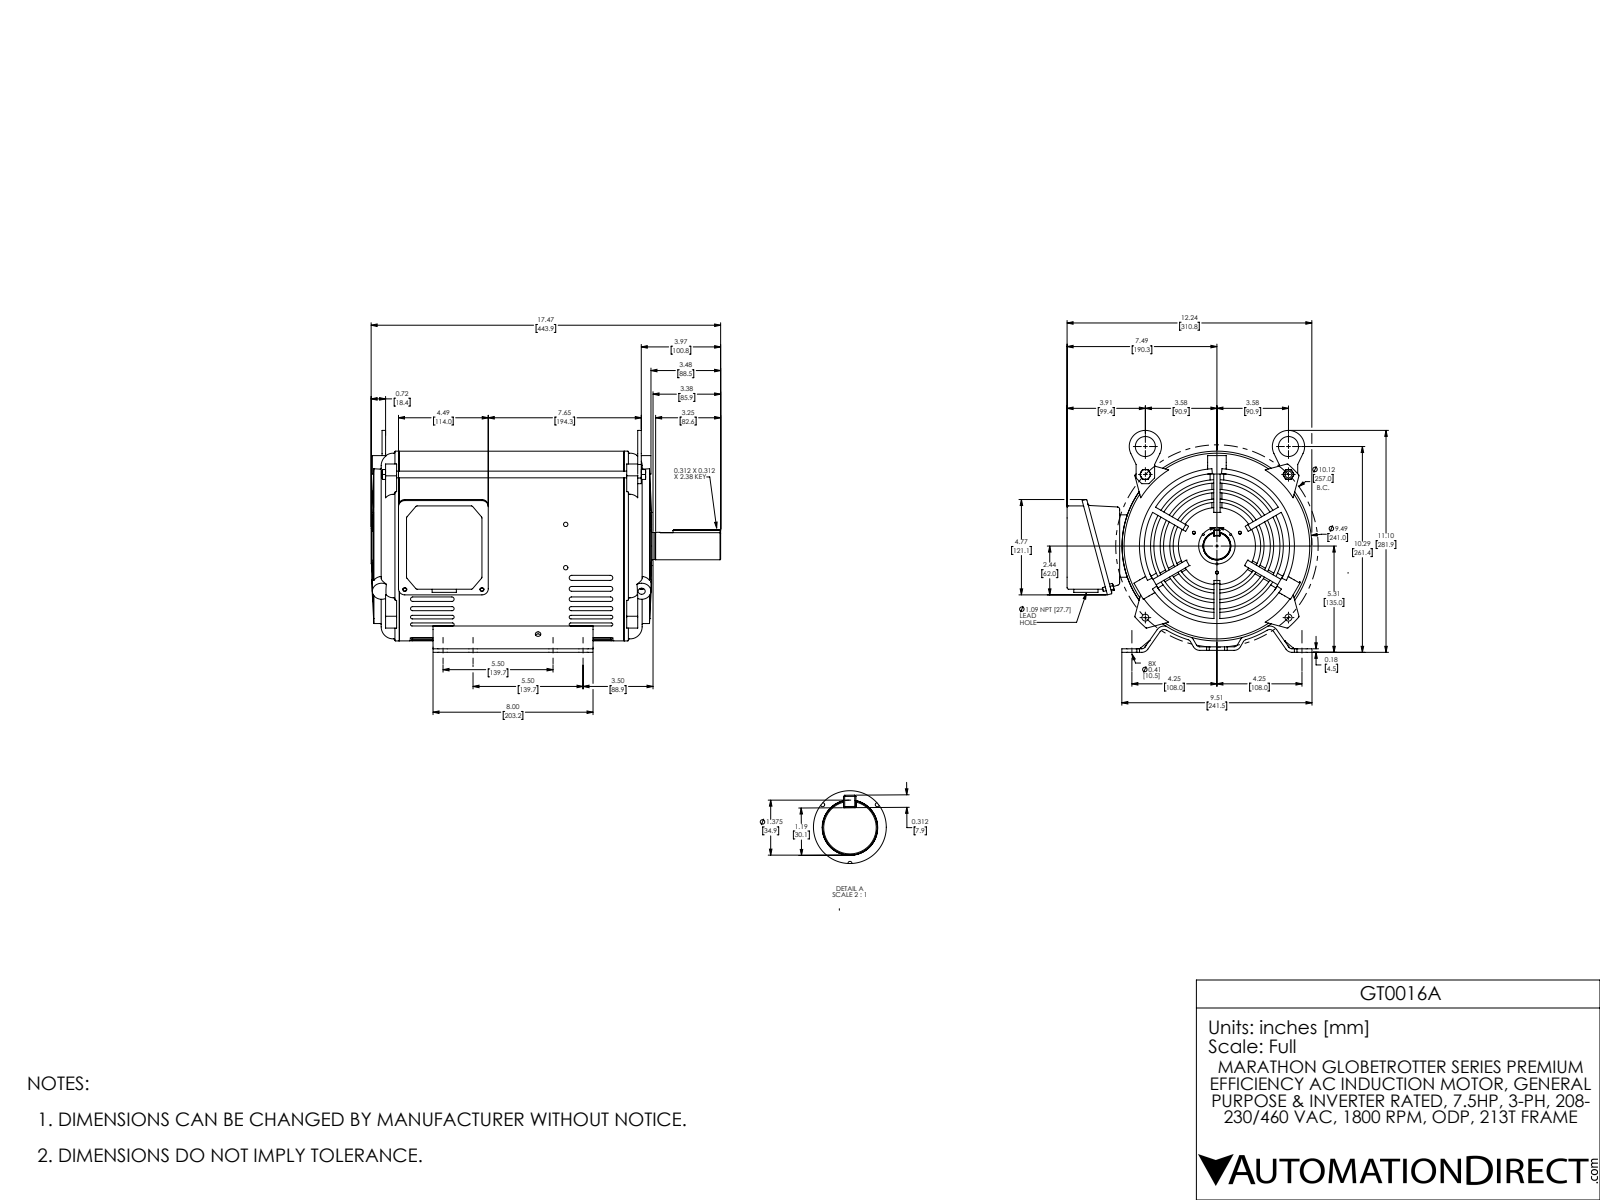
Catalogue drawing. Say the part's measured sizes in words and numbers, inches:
The part is named "SS620684_213T_215T Coord". Its 3-D file was written by "SolidWorks 2017 (AUTOMOTIVE_DESIGN)". It is 25 solids with 1892 faces: 562 planar, 840 cylindrical and 490 other. Overall it measures 17.475 by 12.246 by 11.098 inches. Its volume is 190.3 cubic inches and its surface area 1 652 square inches. Round holes: 10 of diameter 0.374, 8 of diameter 0.413, 5 of diameter 0.217, 4 of diameter 0.252, 4 of diameter 0.315, 4 of diameter 0.343, 4 of diameter 0.358, 3 of diameter 0.101, 2 of diameter 0.276, 2 of diameter 0.335, 2 of diameter 0.5, 2 of diameter 1.004. Round bosses or shafts: 6 of diameter 0.929, 6 of diameter 0.68, 2 of diameter 0.197, 1 of diameter 9.49, 1 of diameter 9.484, 1 of diameter 9.39, 1 of diameter 7.75, 1 of diameter 6.64. Partial cylindrical surfaces (rounded edges, fillets, slot ends): 145 of radius 0.06, 24 of radius 0.118, 24 of radius 0.236, 20 of radius 0.132, 18 of radius 0.25, 16 of radius 0.079, 12 of radius 0.059, 9 of radius 0.197. The main face-to-face distances are 0.177, 0.098, 0.2, 2.63, 0.693, 13.3, 0.276, 0.079, 0.236, 1.38. The hole center spacings are 1, 1.5, 1.565, 2.5, 3.5, 5.5, 6, 1.083.
